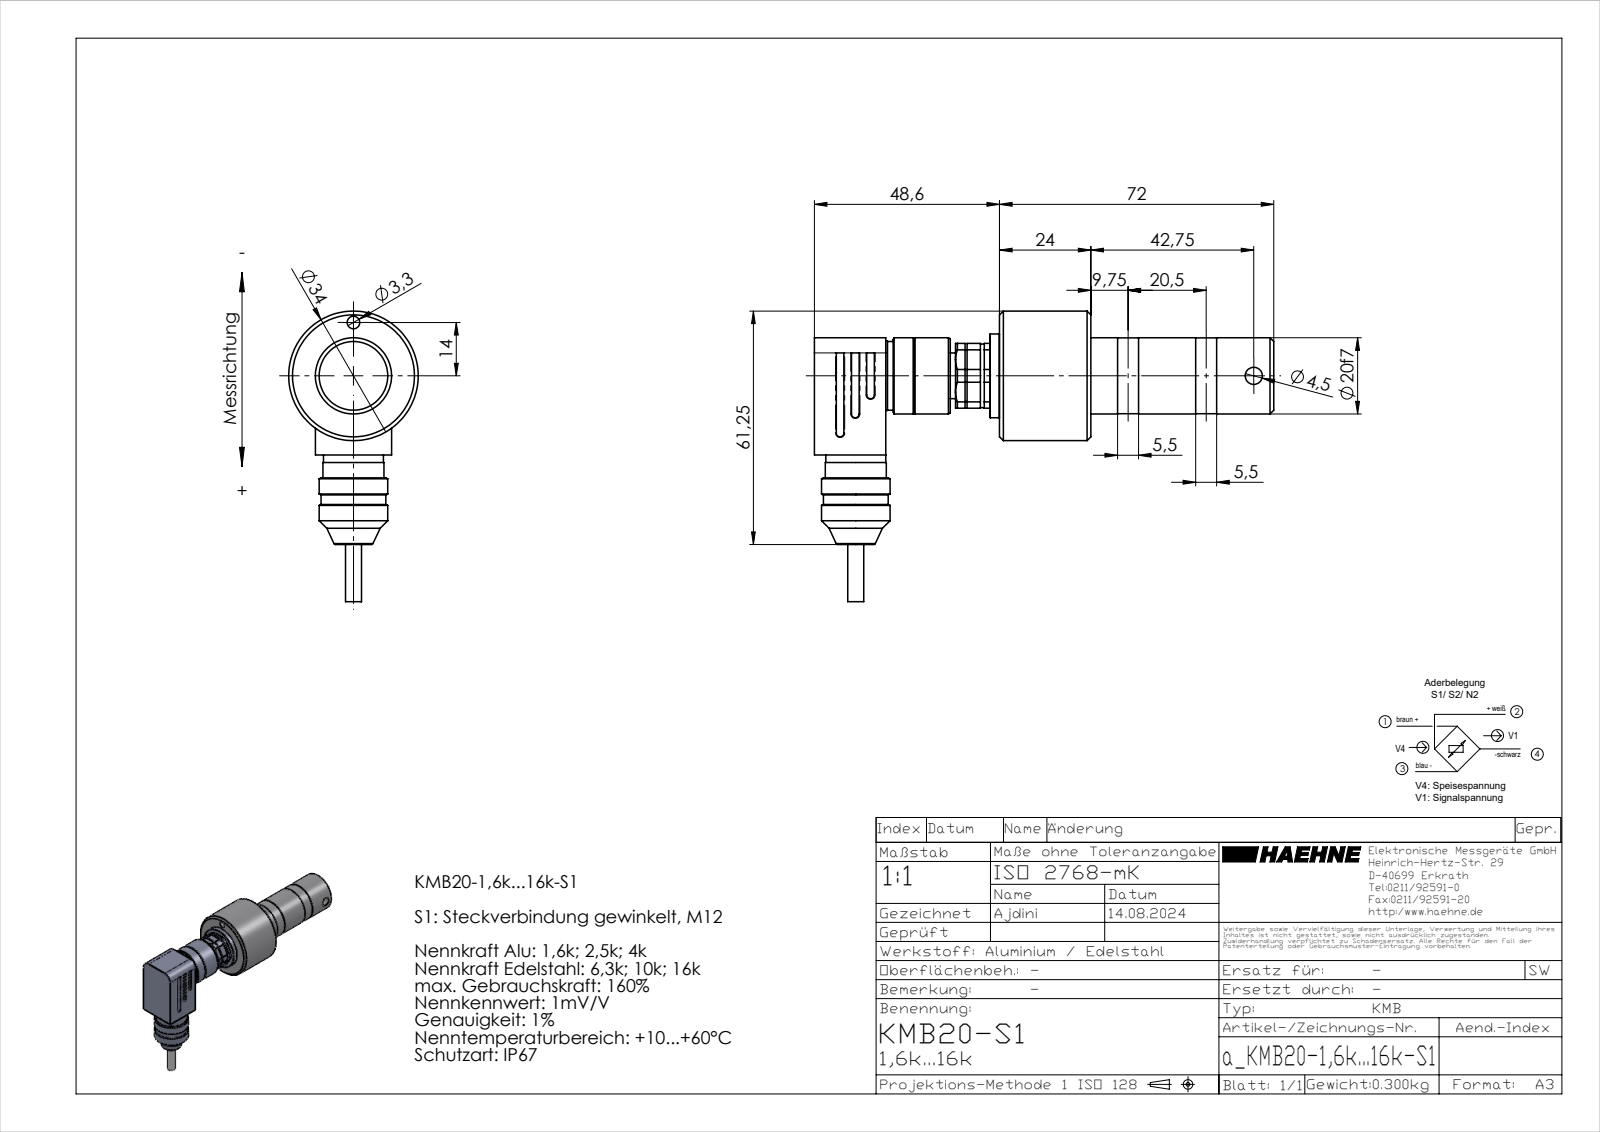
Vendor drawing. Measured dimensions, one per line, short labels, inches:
name: a_KMB20-1,6k...16k-S1
written by: SolidWorks 2023 (AUTOMOTIVE_DESIGN)
unit: in
bodies: 6 solids, 303 faces (132 planar, 122 cylindrical, 49 other)
size: 4.748 × 3.002 × 1.339
volume: 3.768 in³; area: 29.53 in²
holes: 5× ⌀0.024, 2× ⌀0.177, 1× ⌀0.13, 1× ⌀0.236, 1× ⌀0.33, 1× ⌀0.472, 1× ⌀0.557, 1× ⌀0.591
bosses: 4× ⌀0.059, 4× ⌀0.039, 2× ⌀0.709, 2× ⌀0.63, 1× ⌀1.339, 1× ⌀0.866, 1× ⌀0.787, 1× ⌀0.783
rounds: 12× R0.008, 11× R0.039, 6× R0.012, 2× R0.157, 1× R0.022, 1× R0.026, 1× R0.03, 1× R0.138
face distances: 1.913, 1.175, 0.738, 0.945, 2.12, 2.858, 0.787, 0.098, 1.89, 2.835
hole spacings: 0.026, 0.042, 0.042, 0.378, 0.352, 0.353, 0.392, 0.551
